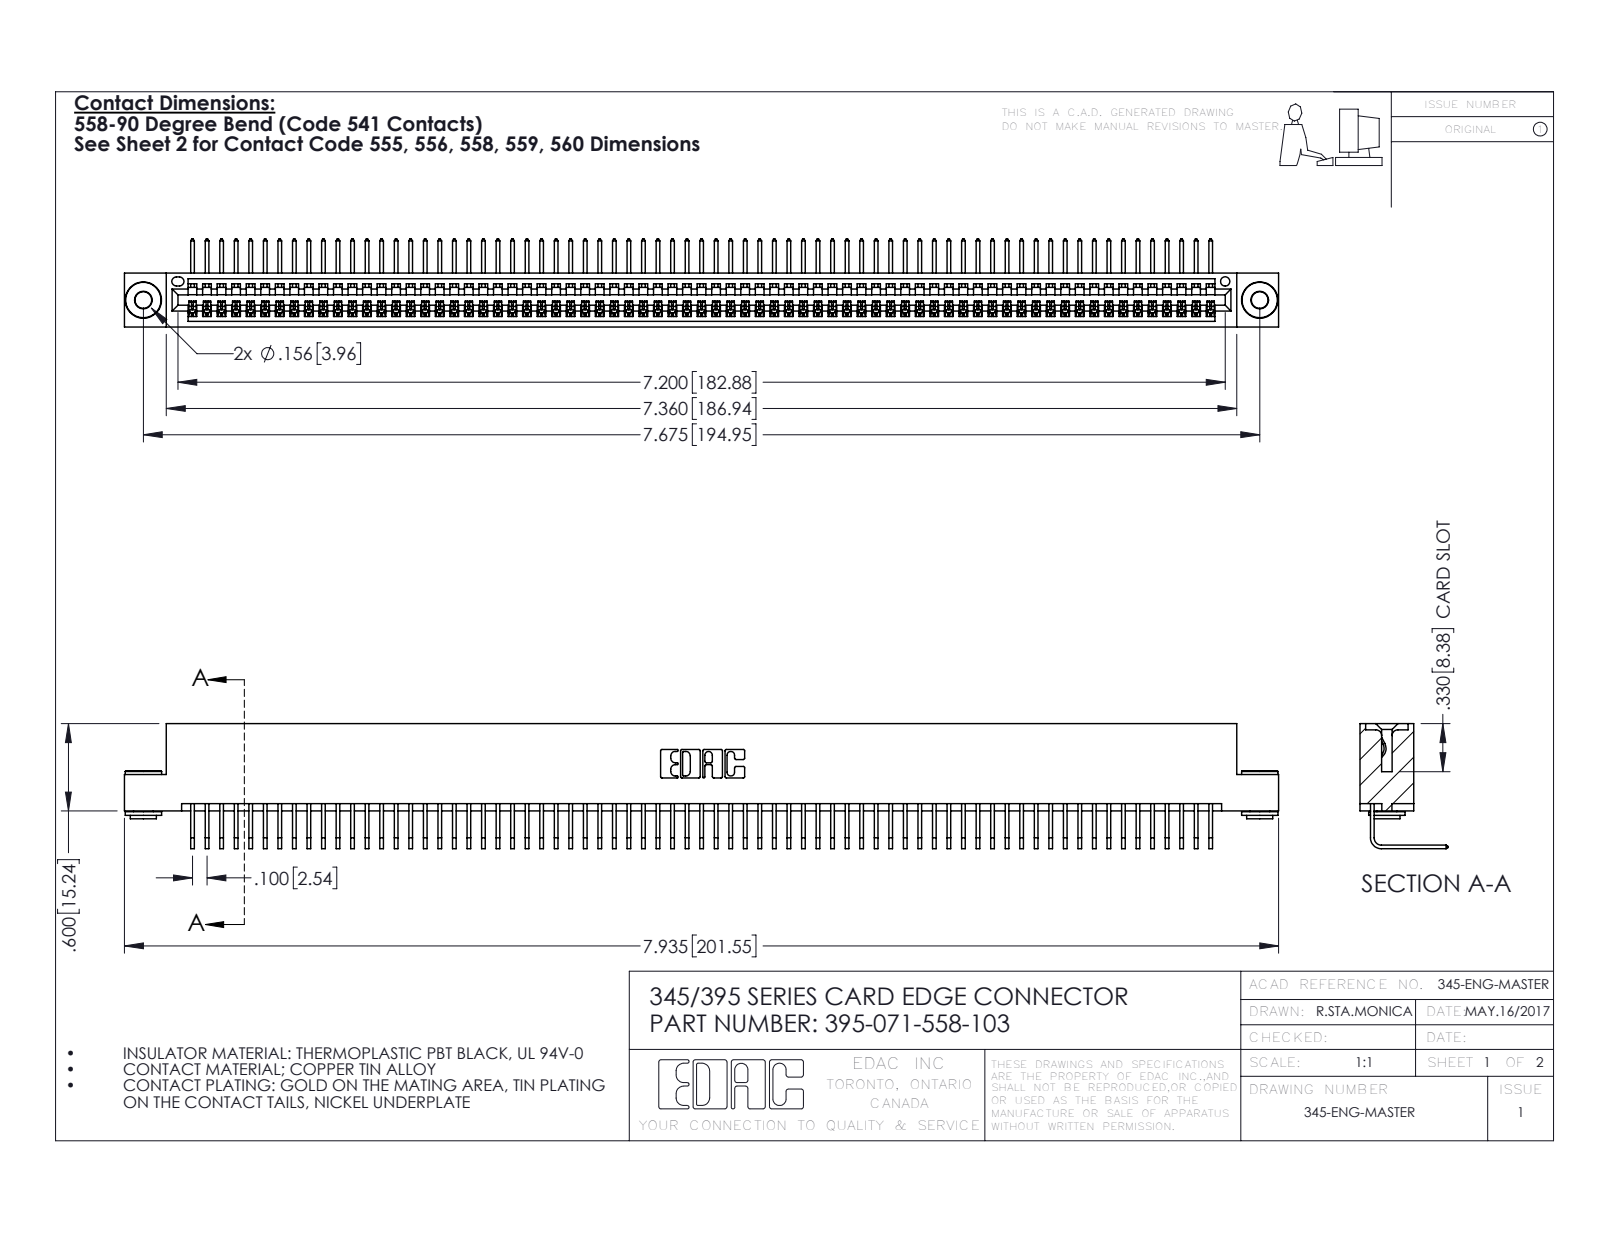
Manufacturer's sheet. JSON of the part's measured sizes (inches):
{"part_name": "395-071-558-103; 345-292-001_558 Tail - 2; 345-250-002_345-250-002-102; 345 Part_Flush Mounting Lugs - 0.156 Dia-TH", "step_written_by": "SolidWorks 2016 (CONFIG_CONTROL_DESIGN)", "units": "inches", "bodies": {"solids": 74, "faces": 4424, "planar": 3072, "cylindrical": 1344, "other": 8}, "overall_size": [7.935, 0.859, 0.605], "volume_in3": 1.198, "surface_area_in2": 43.55, "round_holes": [[0.116, 2], [0.156, 2], [0.064, 1]], "round_bosses_or_shafts": [[0.25, 2], [0.18, 2], [0.136, 2]], "partial_cylinders_radius": [[0.006, 142], [0.01, 22], [0.007, 6], [0.031, 6], [0.026, 3], [0.031, 2], [0.04, 2], [0.014, 1]], "face_to_face_distances": [0.072, 0.298, 0.37, 0.2, 0.025, 0.098, 0.272, 0.225, 0.149, 0.072], "hole_center_spacings": [0.27, 7.439, 7.675]}
